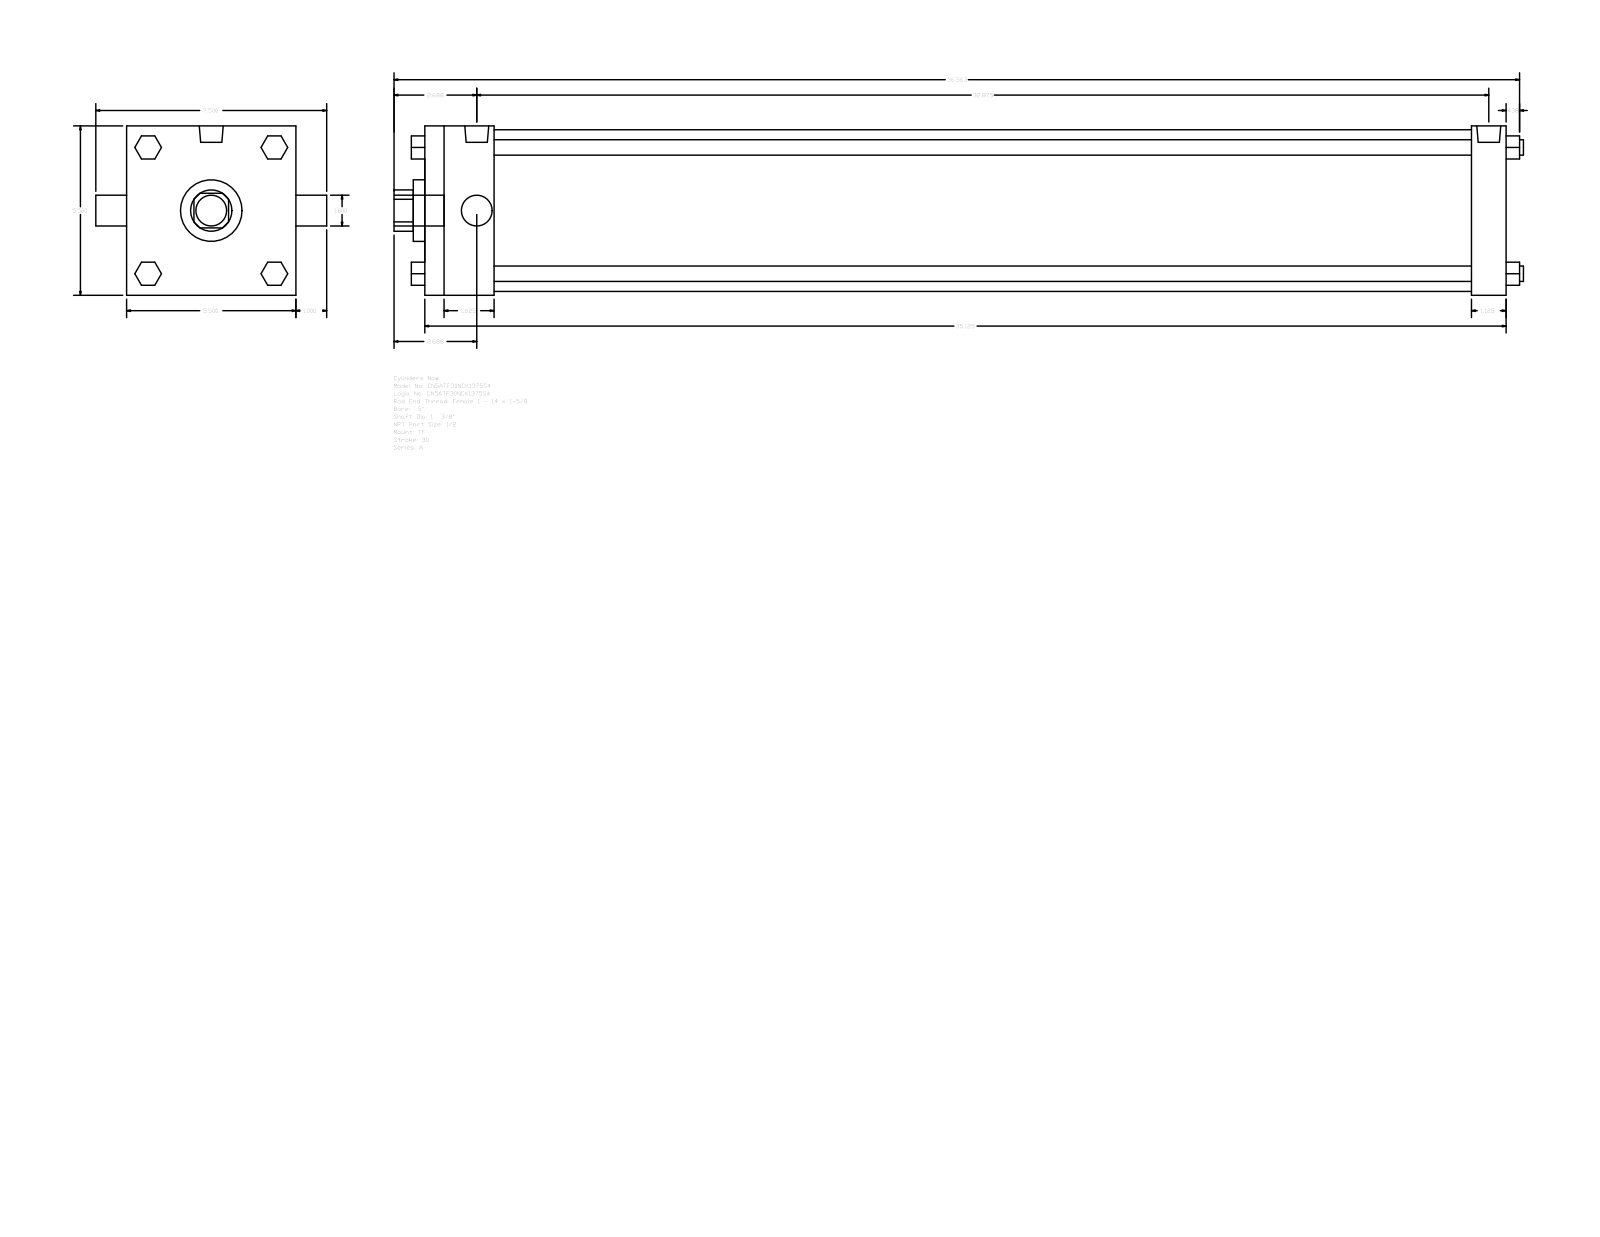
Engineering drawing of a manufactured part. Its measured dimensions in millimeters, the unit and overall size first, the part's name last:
Units: millimetres
Overall size (bounding box): 931.86 × 190.5 × 139.7
Round holes (diameter × count): ⌀25.4 ×1, ⌀34.92 ×1, ⌀50.8 ×1, ⌀133.35 ×1
Round bosses / shafts (diameter × count): ⌀12.7 ×4, ⌀8.73 ×3, ⌀19.77 ×2, ⌀25.4 ×1
Partial cylindrical surfaces — rounded edges, fillets, slot ends (radius × count): R17.06 ×1
Main face-to-face distances: 139.7, 892.18, 28.58, 863.6, 57.15, 806.45, 835.03, 19.05, 52.07, 90.18
Bodies: 0 solids, 120 faces (92 planar, 28 cylindrical, 0 other)
Part name (STEP PRODUCT): A_TF__0500_1.375
STEP written by: GSSL Pune (CONFIG_CONTROL_DESIGN)
